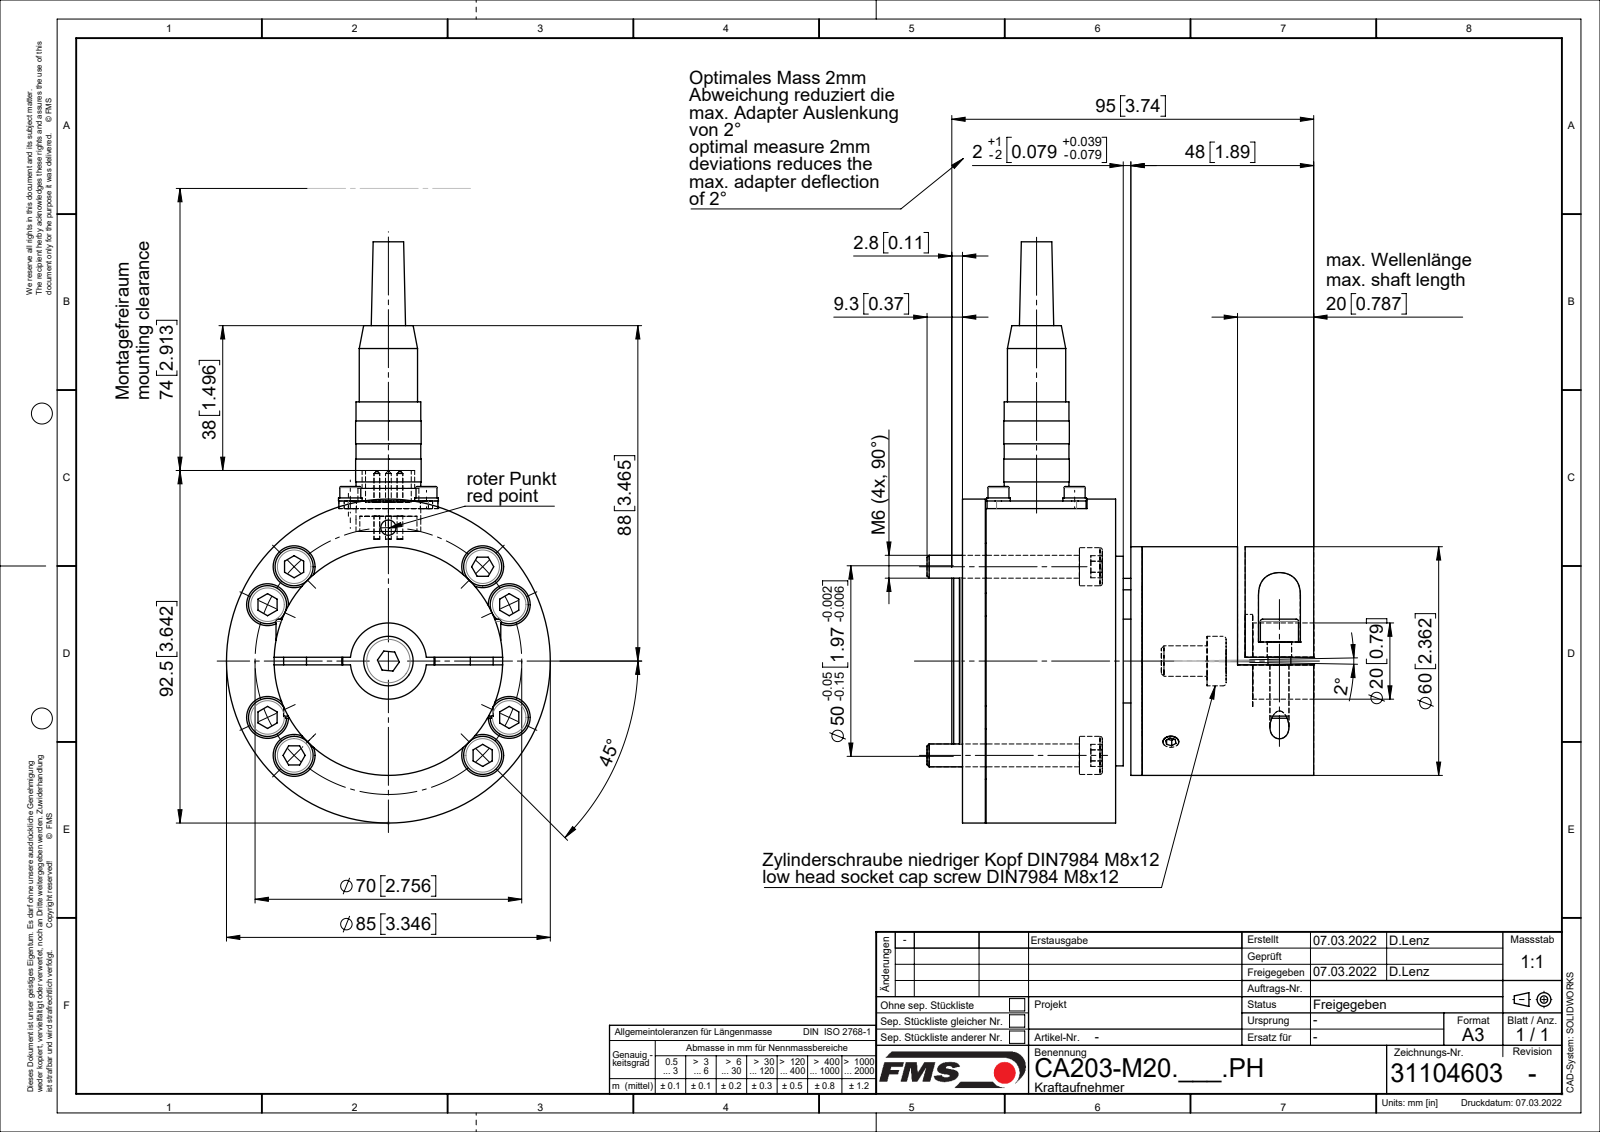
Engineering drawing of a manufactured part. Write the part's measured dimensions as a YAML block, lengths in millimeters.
part_name: "070907-4_01; Zyl-Schr DIN912_M3x6; 31104424_01; 31104422_01 (+8 more)"
step_written_by: "SolidWorks 2018 (CONFIG_CONTROL_DESIGN)"
units: millimeters
bodies: {solids: 44, faces: 828, planar: 296, cylindrical: 337, other: 195}
overall_size: [152.5, 101.5, 85]
volume: 305161
surface_area: 110049
round_holes:
  - {diameter: 2.5, count: 8}
  - {diameter: 6.5, count: 8}
  - {diameter: 11, count: 8}
  - {diameter: 5, count: 6}
  - {diameter: 4, count: 5}
  - {diameter: 3.1, count: 4}
  - {diameter: 3.2, count: 4}
  - {diameter: 3.6, count: 4}
  - {diameter: 7, count: 4}
  - {diameter: 6.4, count: 2}
  - {diameter: 3, count: 1}
  - {diameter: 4.2, count: 1}
round_bosses_or_shafts:
  - {diameter: 6, count: 11}
  - {diameter: 10, count: 10}
  - {diameter: 3, count: 8}
  - {diameter: 1.5, count: 5}
  - {diameter: 6.2, count: 4}
  - {diameter: 5.7, count: 4}
  - {diameter: 5.5, count: 4}
  - {diameter: 85, count: 1}
partial_cylinders:
  - {radius: 2.5, count: 4}
  - {radius: 5, count: 2}
  - {radius: 5.5, count: 2}
face_to_face_distances: [2, 41, 30, 45, 6, 10, 50, 34, 3, 12]
hole_center_spacings: [35, 20, 24.78, 25.2, 32.8, 51.14, 56.46, 28.28]
